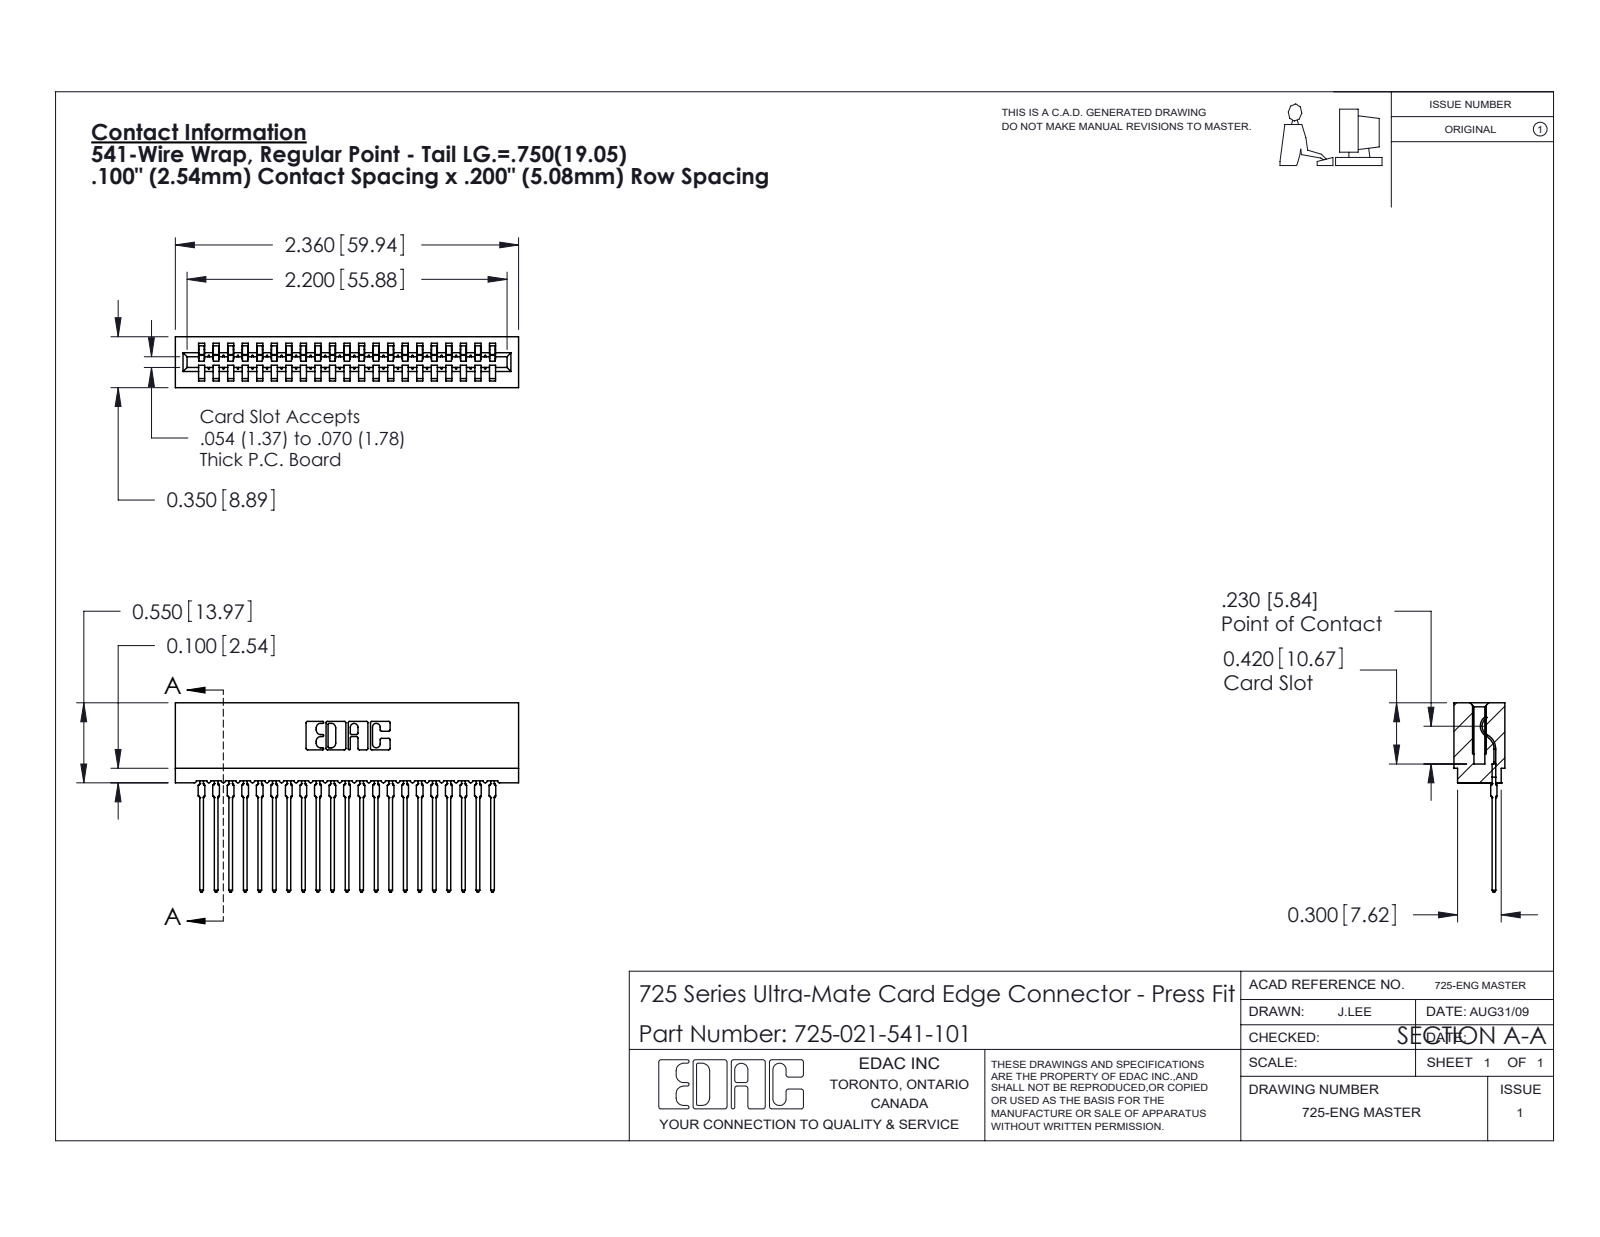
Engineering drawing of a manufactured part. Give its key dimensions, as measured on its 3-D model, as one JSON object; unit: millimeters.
{"part_name": "725-021-541-101; 725 Part_Insulator Option - 01; 745-292-001_541", "step_written_by": "SolidWorks 2020 (CONFIG_CONTROL_DESIGN)", "units": "millimeters", "bodies": {"solids": 22, "faces": 2447, "planar": 1462, "cylindrical": 439, "other": 546}, "overall_size": [59.9, 33, 8.9], "volume_mm3": 4750, "surface_area_mm2": 9181, "partial_cylinders_radius": [[0.4, 42], [0.5, 42], [0.3, 22], [0.2, 6], [0.8, 6], [0.1, 4], [0.3, 4], [0.7, 3]], "face_to_face_distances": [5.1, 2.5, 7.6, 10.2, 12.7, 15.2, 17.8, 8.9, 20.3, 1.6]}
